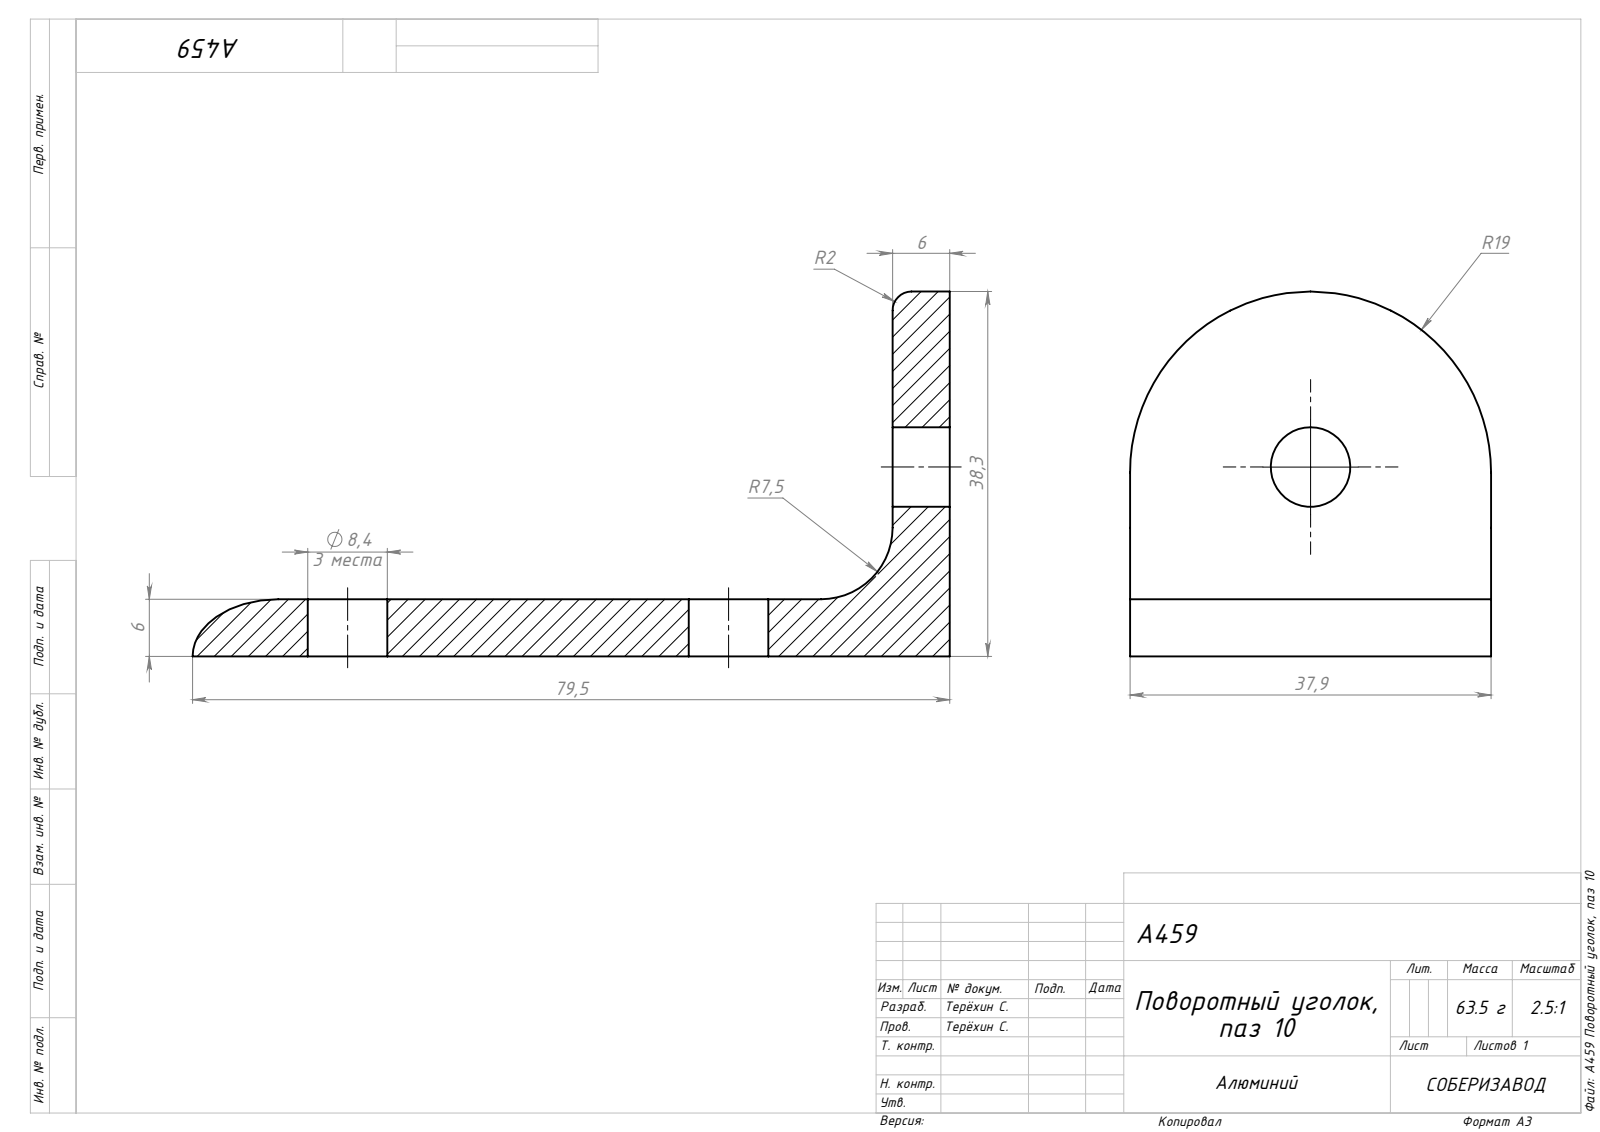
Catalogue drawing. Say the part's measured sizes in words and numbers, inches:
The part is named "A458 Поворотный уголок, паз 8". Its 3-D file was written by "SolidWorks 2021 (AUTOMOTIVE_DESIGN)". It is 1 solid with 17 faces: 6 planar, 10 cylindrical and 1 other. Overall it measures 3.13 by 1.508 by 1.492 inches. Its volume is 1.435 cubic inches and its surface area 15.13 square inches. Round holes: 3 of diameter 0.329. Partial cylindrical surfaces (rounded edges, fillets, slot ends): 2 of radius 0.748, 1 of radius 0.079, 1 of radius 0.295. The main face-to-face distances are 0.236, 1.492. The hole center spacings are 1.575.
